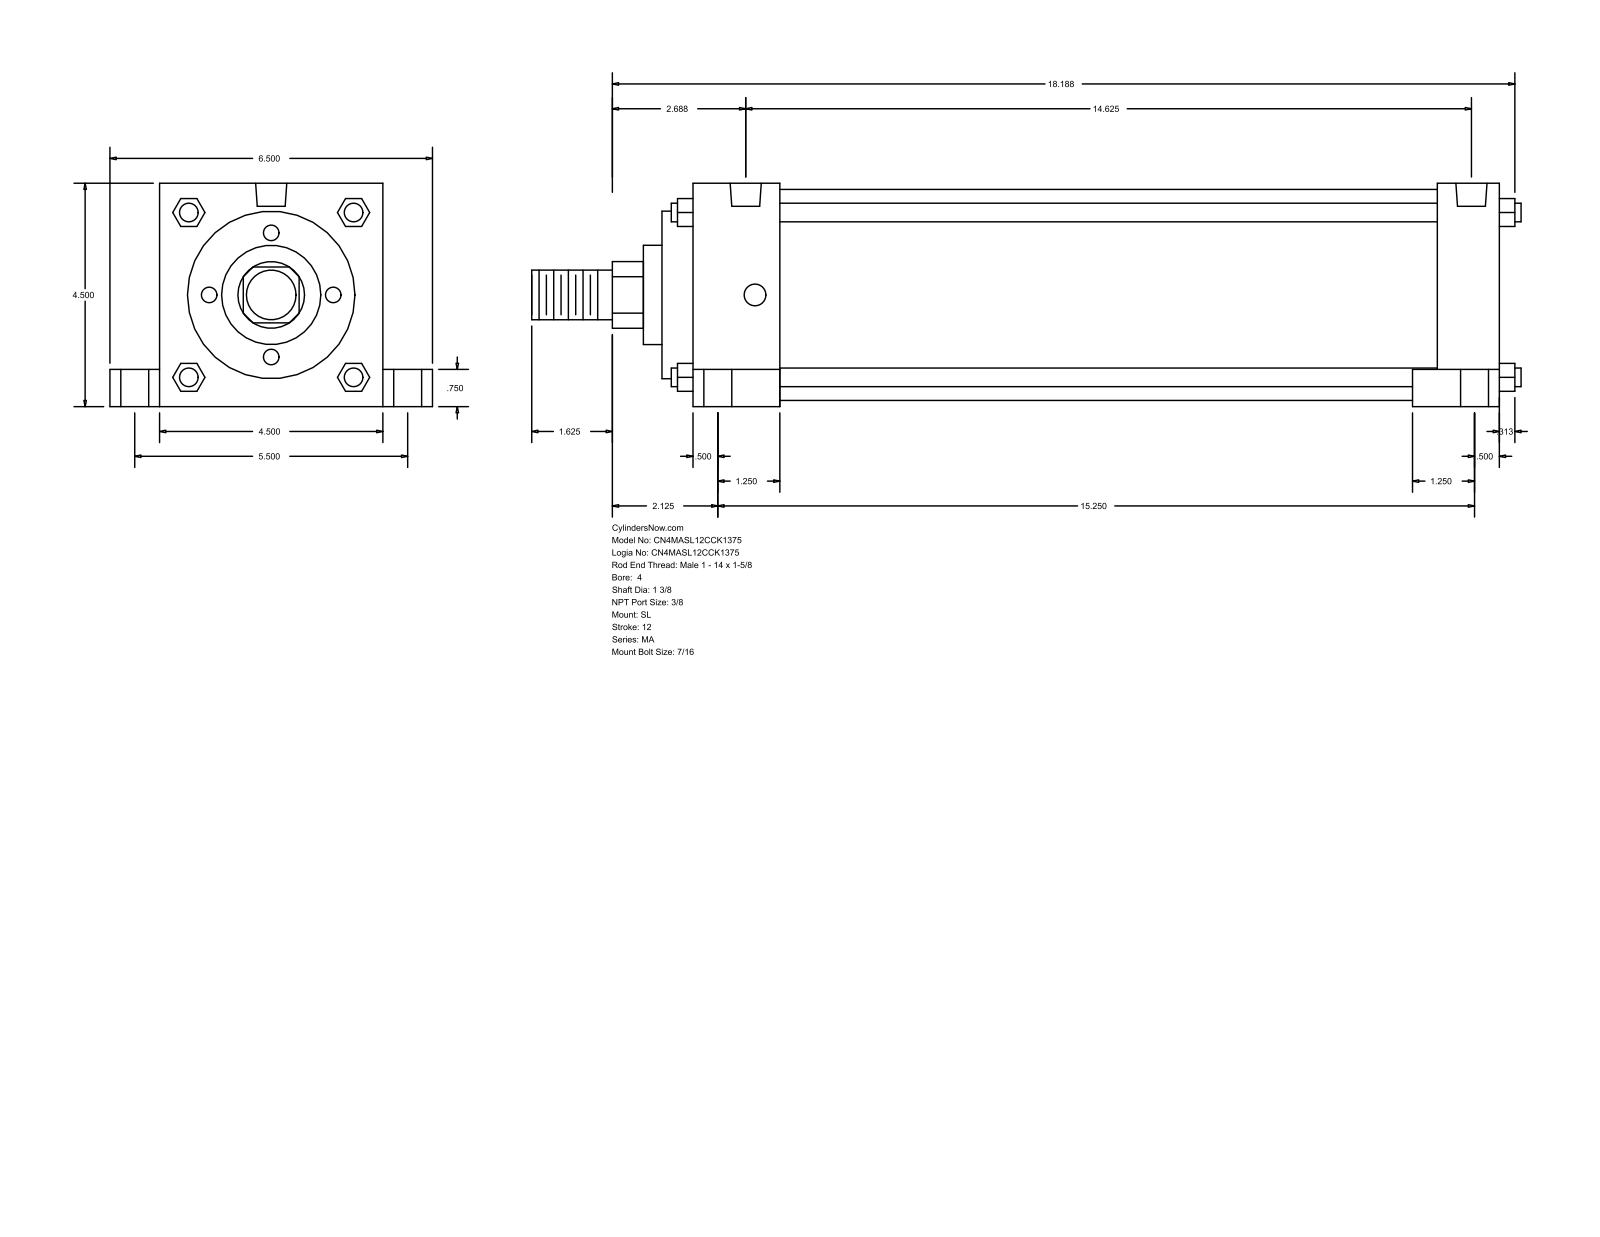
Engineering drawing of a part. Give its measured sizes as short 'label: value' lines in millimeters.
name: MA_SL__0400_1.375
written by: GSSL Pune (CONFIG_CONTROL_DESIGN)
unit: mm
bodies: 0 solids, 150 faces (113 planar, 37 cylindrical, 0 other)
size: 506.41 × 165.1 × 114.3
holes: 4× ⌀11.11, 4× ⌀14.29, 4× ⌀20.64, 2× ⌀15.93
bosses: 4× ⌀9.53, 1× ⌀107.95, 1× ⌀85.72, 1× ⌀50.8, 1× ⌀34.92, 1× ⌀25.4
rounds: 1× R17.06
face distances: 114.3, 412.75, 336.55, 428.62, 15.87, 60.32, 44.45, 368.3, 396.87, 381
hole spacings: 69.87, 70.14, 71.29, 72.4, 139.7, 361.95, 374.86, 379.54
